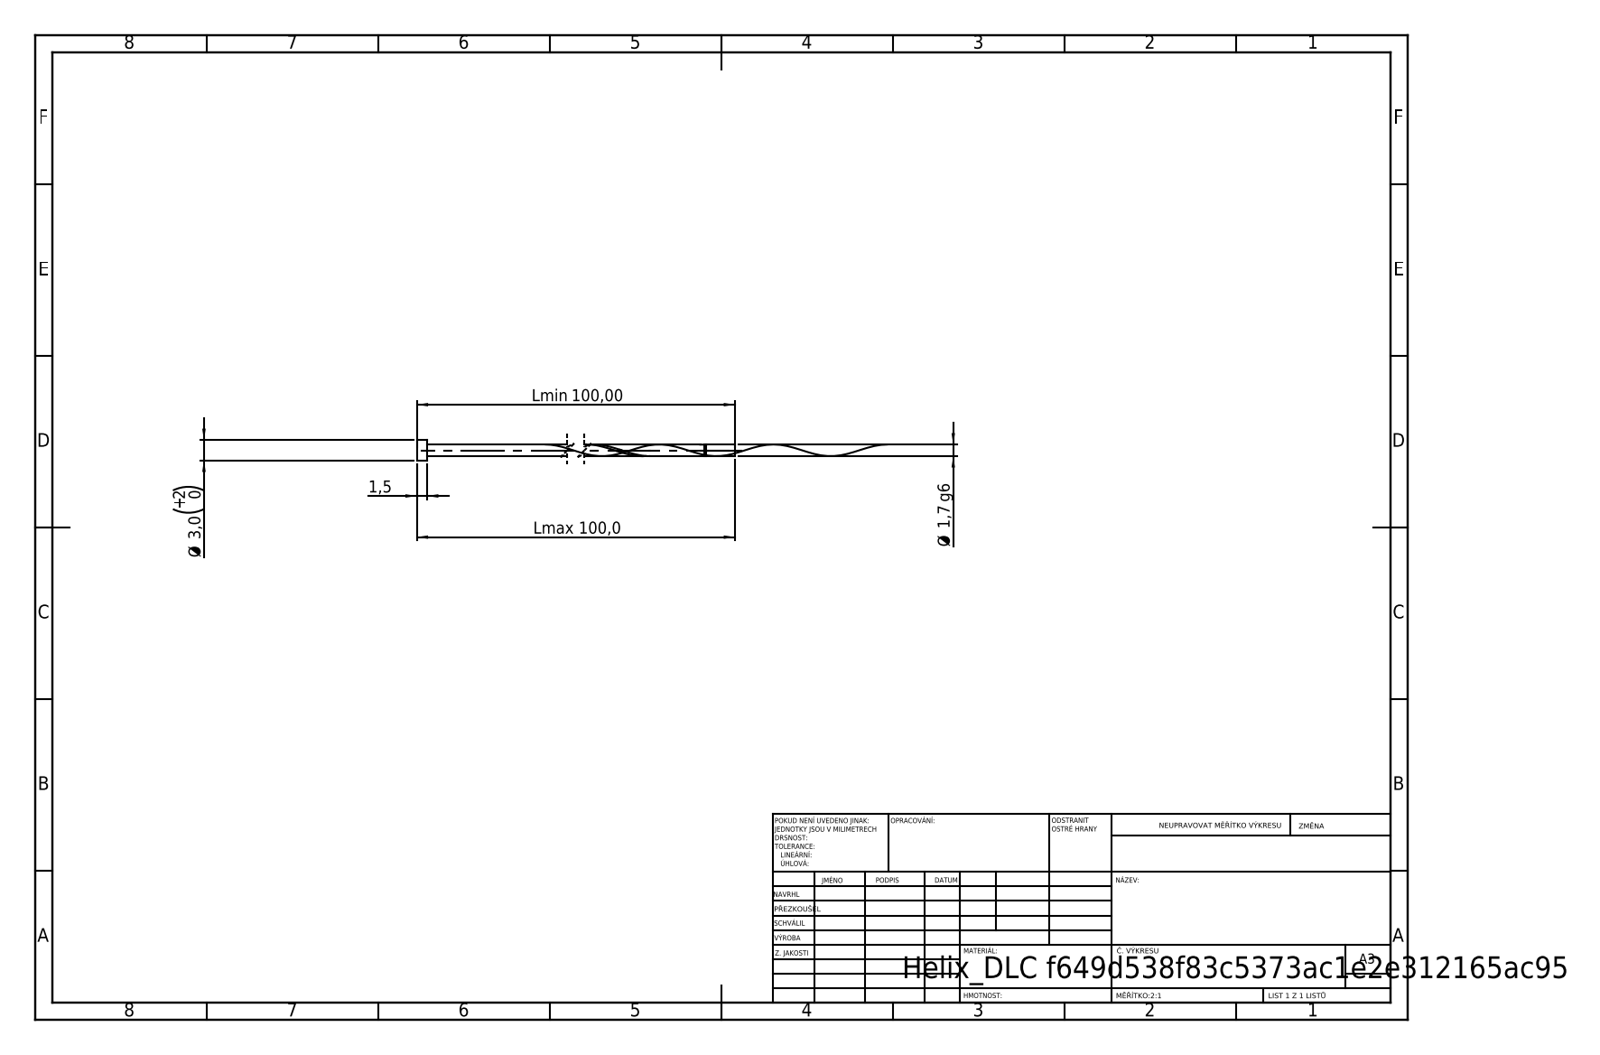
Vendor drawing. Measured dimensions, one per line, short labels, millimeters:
written by: SolidWorks 2019 (CONFIG_CONTROL_DESIGN)
unit: mm
bodies: 1 solid, 16 faces (6 planar, 9 cylindrical, 1 other)
size: 100 × 3 × 3
volume: 282 mm³; area: 742 mm²
bosses: 1× ⌀3, 1× ⌀1.7, 1× ⌀1.36
face distances: 1.5, 100, 98.5, 95.8, 94.3, 4.2, 95.46, 93.96, 0.34, 4.54
